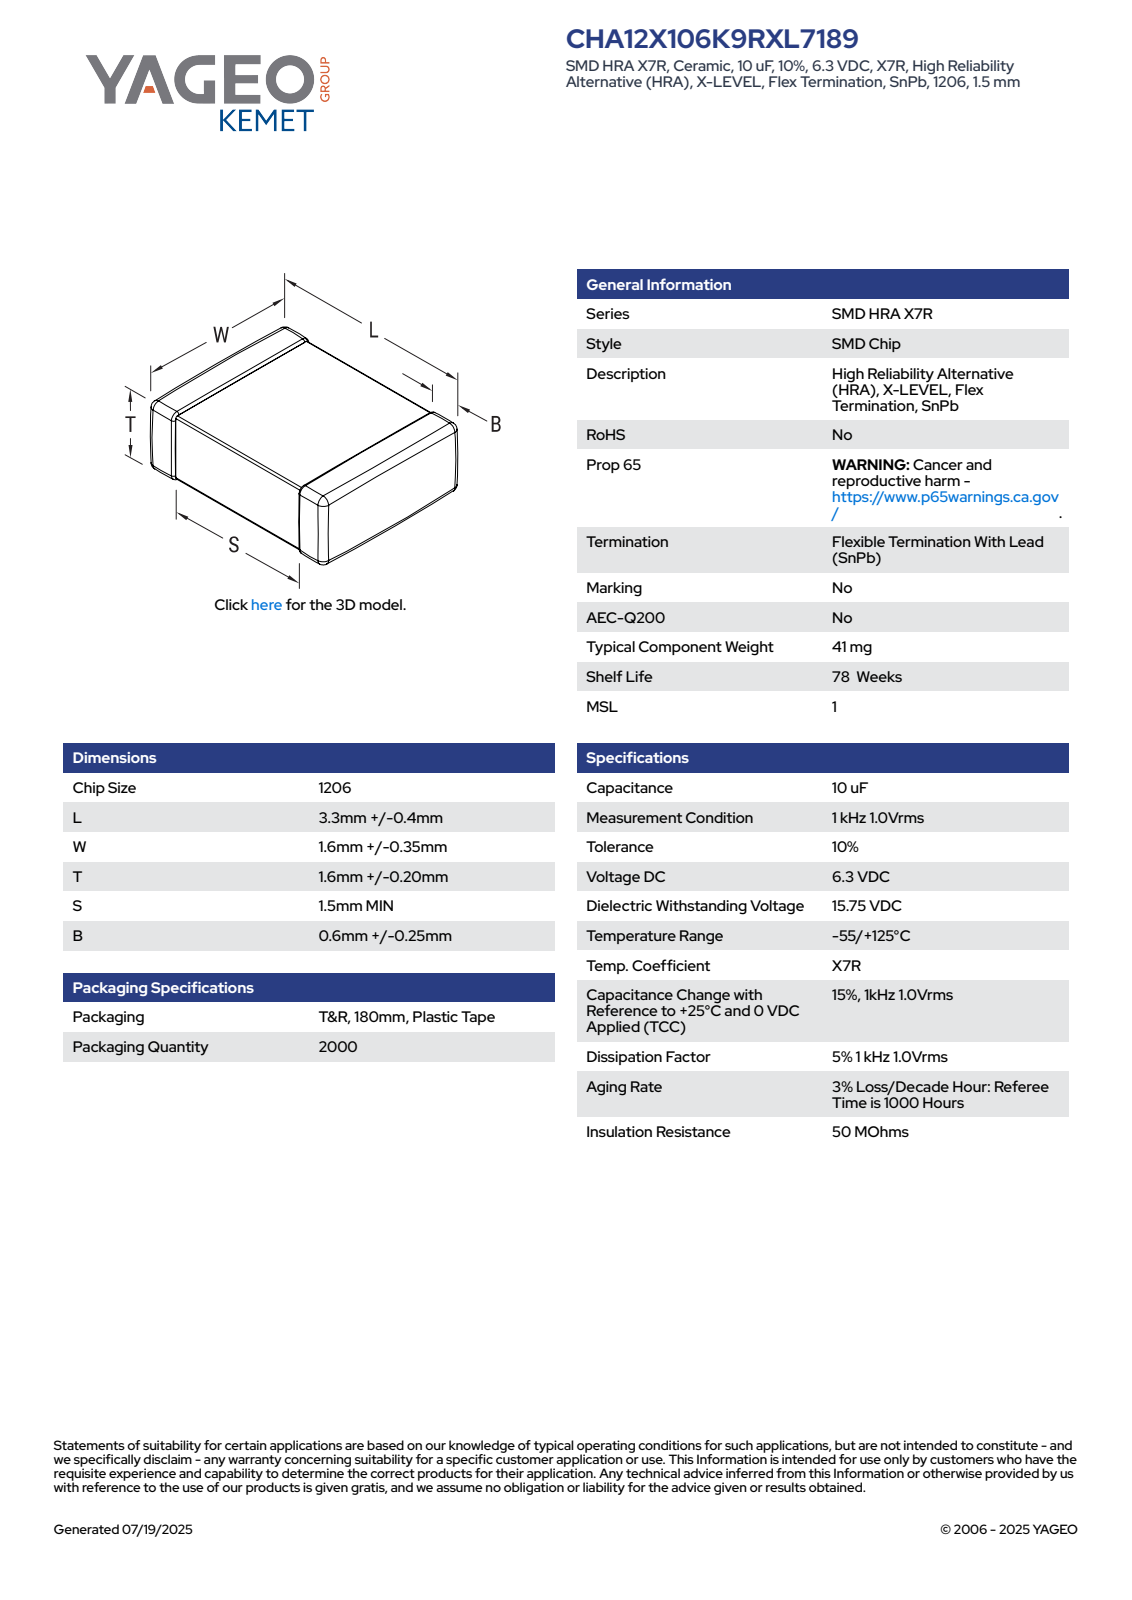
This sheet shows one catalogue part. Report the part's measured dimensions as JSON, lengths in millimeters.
{"part_name": "CCSM_STD_1206_L3.7W1.95T1.8S1.6B0.85", "step_written_by": "SolidWorks 2021 (AUTOMOTIVE_DESIGN)", "units": "millimeters", "bodies": {"solids": 4, "faces": 125, "planar": 71, "cylindrical": 38, "other": 16}, "overall_size": [3.7, 1.95, 1.8], "volume_mm3": 12, "surface_area_mm2": 34, "face_to_face_distances": [1.76, 1.91, 1.72, 1.87, 3.7, 1.8, 1.95, 1.71, 1.99, 2]}
